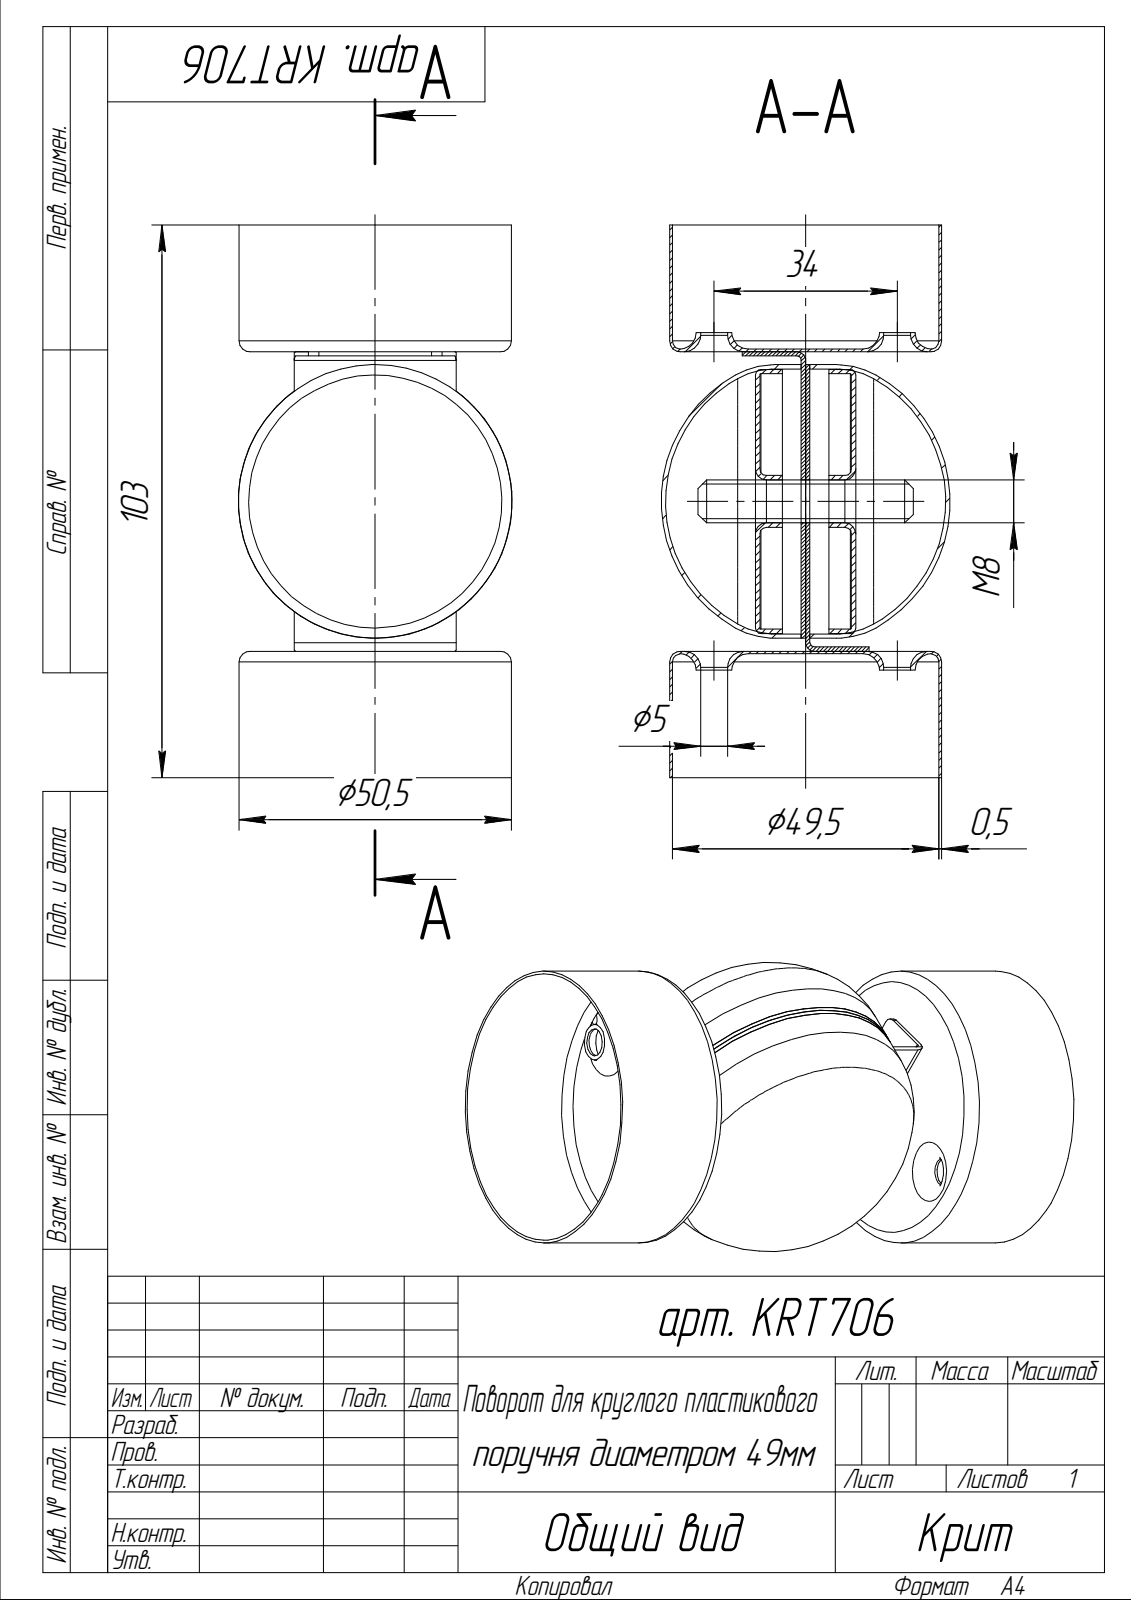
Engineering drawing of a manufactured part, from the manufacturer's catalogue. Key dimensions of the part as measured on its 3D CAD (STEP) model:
Part name (STEP PRODUCT): арт. KRT706.001; арт. KRT706.004; арт. KRT706; арт. KRT706.002 (+2 more)
STEP written by: SolidWorks 2014 (AUTOMOTIVE_DESIGN)
Units: millimetres
Bodies: 8 solids, 160 faces (38 planar, 64 cylindrical, 58 other)
Overall size (bounding box): 102.6 × 53.6 × 50.8
Volume: 20 197 mm³ · Surface area: 59 495 mm²
Round holes (diameter × count): ⌀5 ×2, ⌀8 ×1, ⌀47.4 ×1, ⌀49.2 ×1, ⌀49.5 ×1
Round bosses / shafts (diameter × count): ⌀50.8 ×1, ⌀50.5 ×1, ⌀49 ×1, ⌀9.6 ×1
Partial cylindrical surfaces — rounded edges, fillets, slot ends (radius × count): R2 ×4, R0.8 ×2, R1.6 ×2, R3.3 ×2
Main face-to-face distances: 0.8, 8.5, 9.3, 10.1, 17.8, 7.7, 0.5, 56.1, 1.6, 55.6
Hole centre spacings: 17, 34
